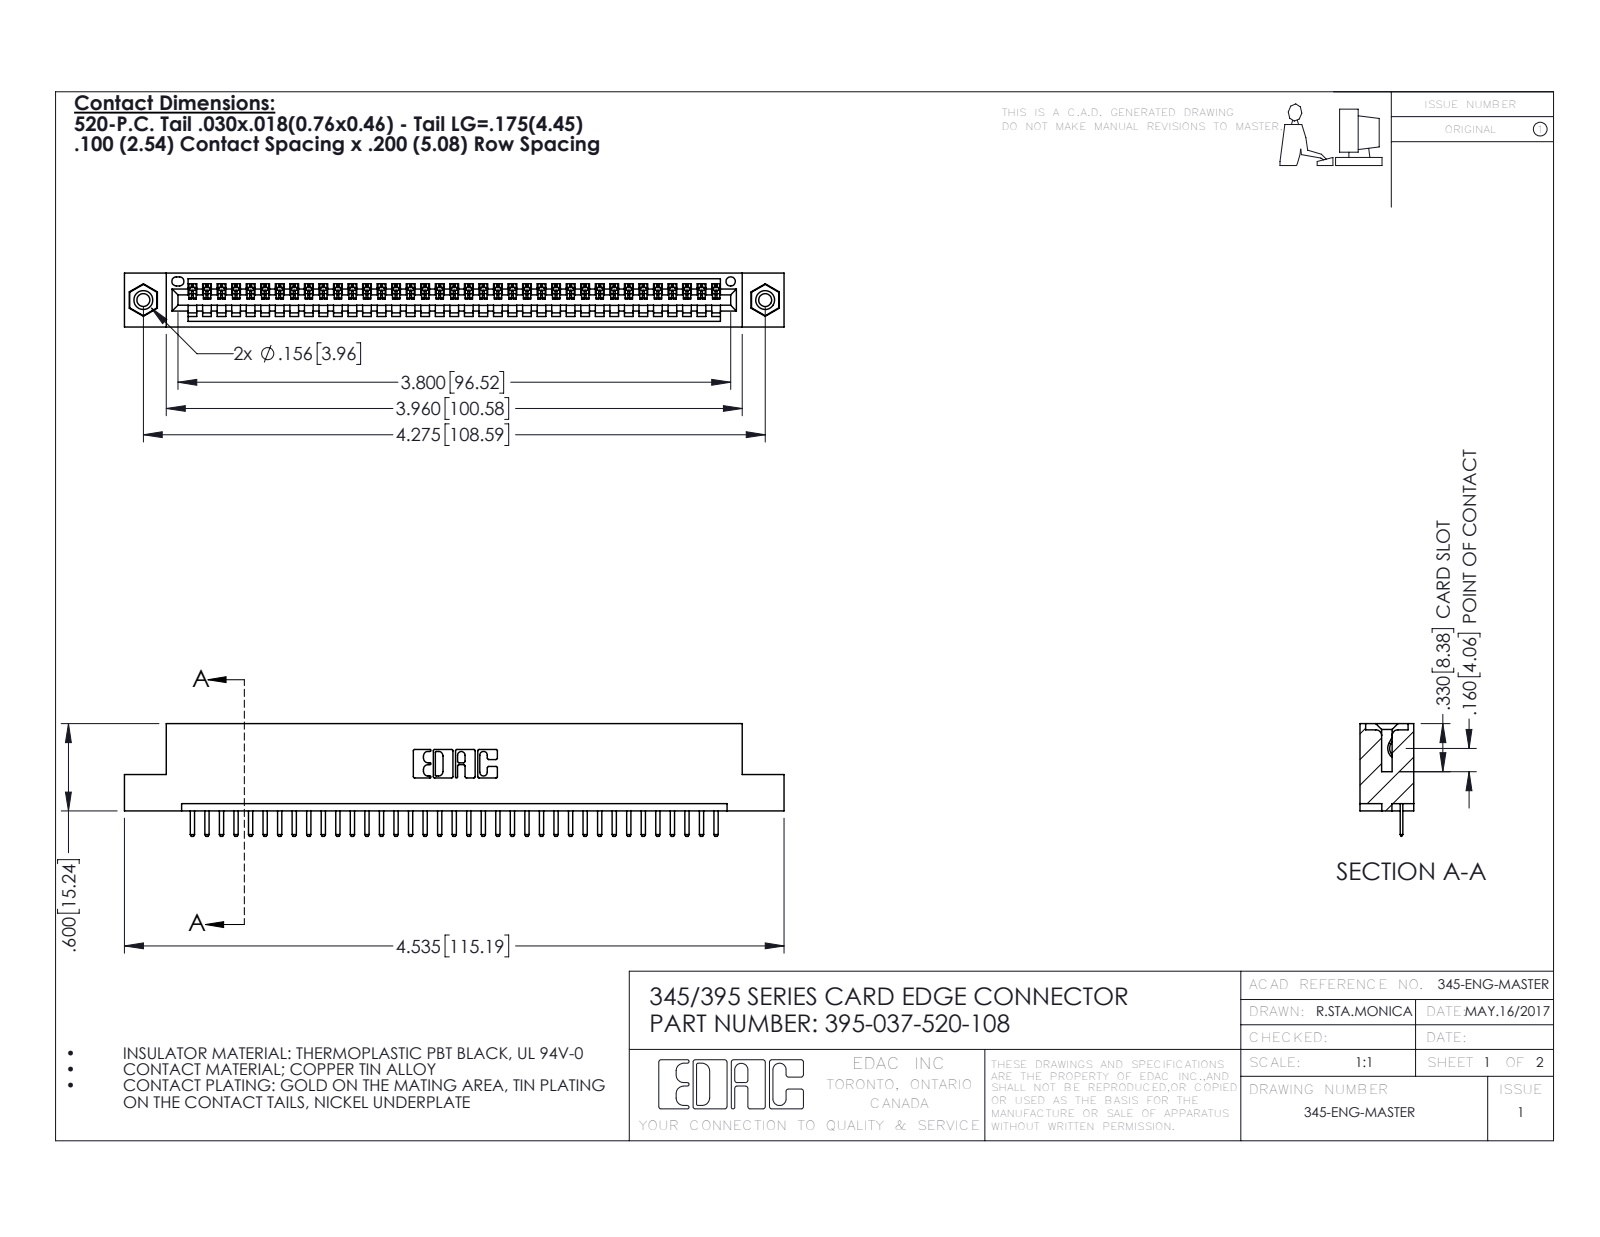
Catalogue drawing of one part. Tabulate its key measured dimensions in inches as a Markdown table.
| quantity | value |
| --- | --- |
| part name | 345 Part_Flush Mounting Lugs - 0.156 Dia-TI; 345-292-001_345-293-120; 395-037-520-108; 345-250-001_345-250-003-102 |
| STEP written by | SolidWorks 2016 (CONFIG_CONTROL_DESIGN) |
| units | inches |
| bodies | 40 solids, 2480 faces (1666 planar, 798 cylindrical, 16 other) |
| overall size | 4.535 × 0.775 × 0.37 |
| volume | 0.658 in³ |
| surface area | 21.6 in² |
| round holes (diameter × count) | 0.089 × 2, 0.125 × 2, 0.156 × 2, 0.064 × 1 |
| round bosses / shafts (diameter × count) | 0.155 × 2 |
| partial cylindrical surfaces (radius × count) | 0.01 × 76, 0.006 × 74, 0.01 × 22, 0.007 × 6, 0.031 × 6, 0.026 × 3, 0.031 × 2, 0.04 × 2 |
| main face-to-face distances | 0.072, 0.298, 0.37, 0.2, 0.098, 0.272, 0.025, 0.225, 0.072, 0.149 |
| hole center spacings | 0.27, 4.039, 4.275 |
